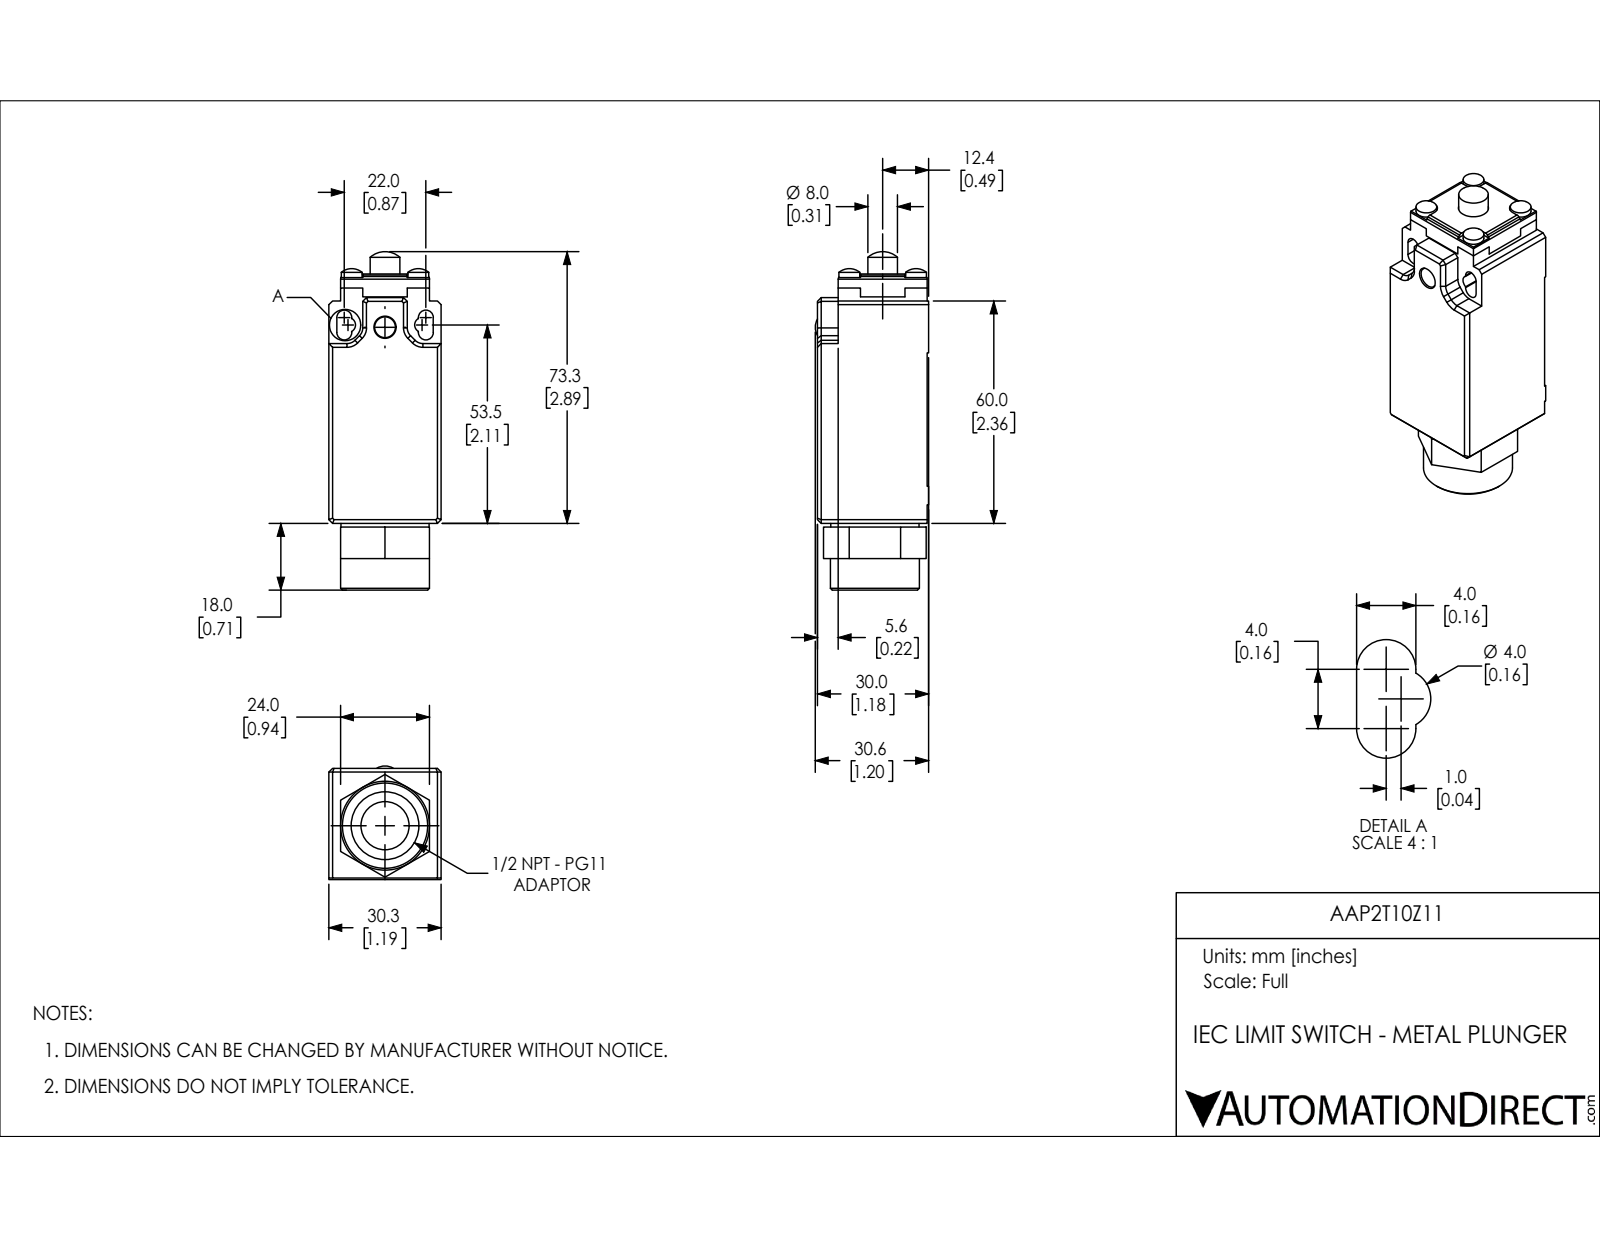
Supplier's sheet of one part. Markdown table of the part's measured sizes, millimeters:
| quantity | value |
| --- | --- |
| part name | AAP2T10Z11 |
| STEP written by | SolidWorks 2018 (AUTOMOTIVE_DESIGN) |
| units | millimeters |
| bodies | 5 solids, 218 faces (117 planar, 76 cylindrical, 25 other) |
| overall size | 91.3 × 30.6 × 30.3 |
| volume | 56 600 mm³ |
| surface area | 17 590 mm² |
| round holes (diameter × count) | 6 × 1, 8.1 × 1, 13 × 1, 17 × 1, 18.3 × 1, 18.8 × 1, 19 × 1 |
| round bosses / shafts (diameter × count) | 5.6 × 5, 24 × 1, 23.8 × 1, 18.4 × 1, 8 × 1 |
| partial cylindrical surfaces (radius × count) | 1 × 8, 3 × 8, 2 × 6, 10 × 1, 10.2 × 1 |
| main face-to-face distances | 30.3, 29.6, 24, 61.1, 1, 0.4, 3.1, 27.2, 30, 18 |
| hole center spacings | 2.1 |
